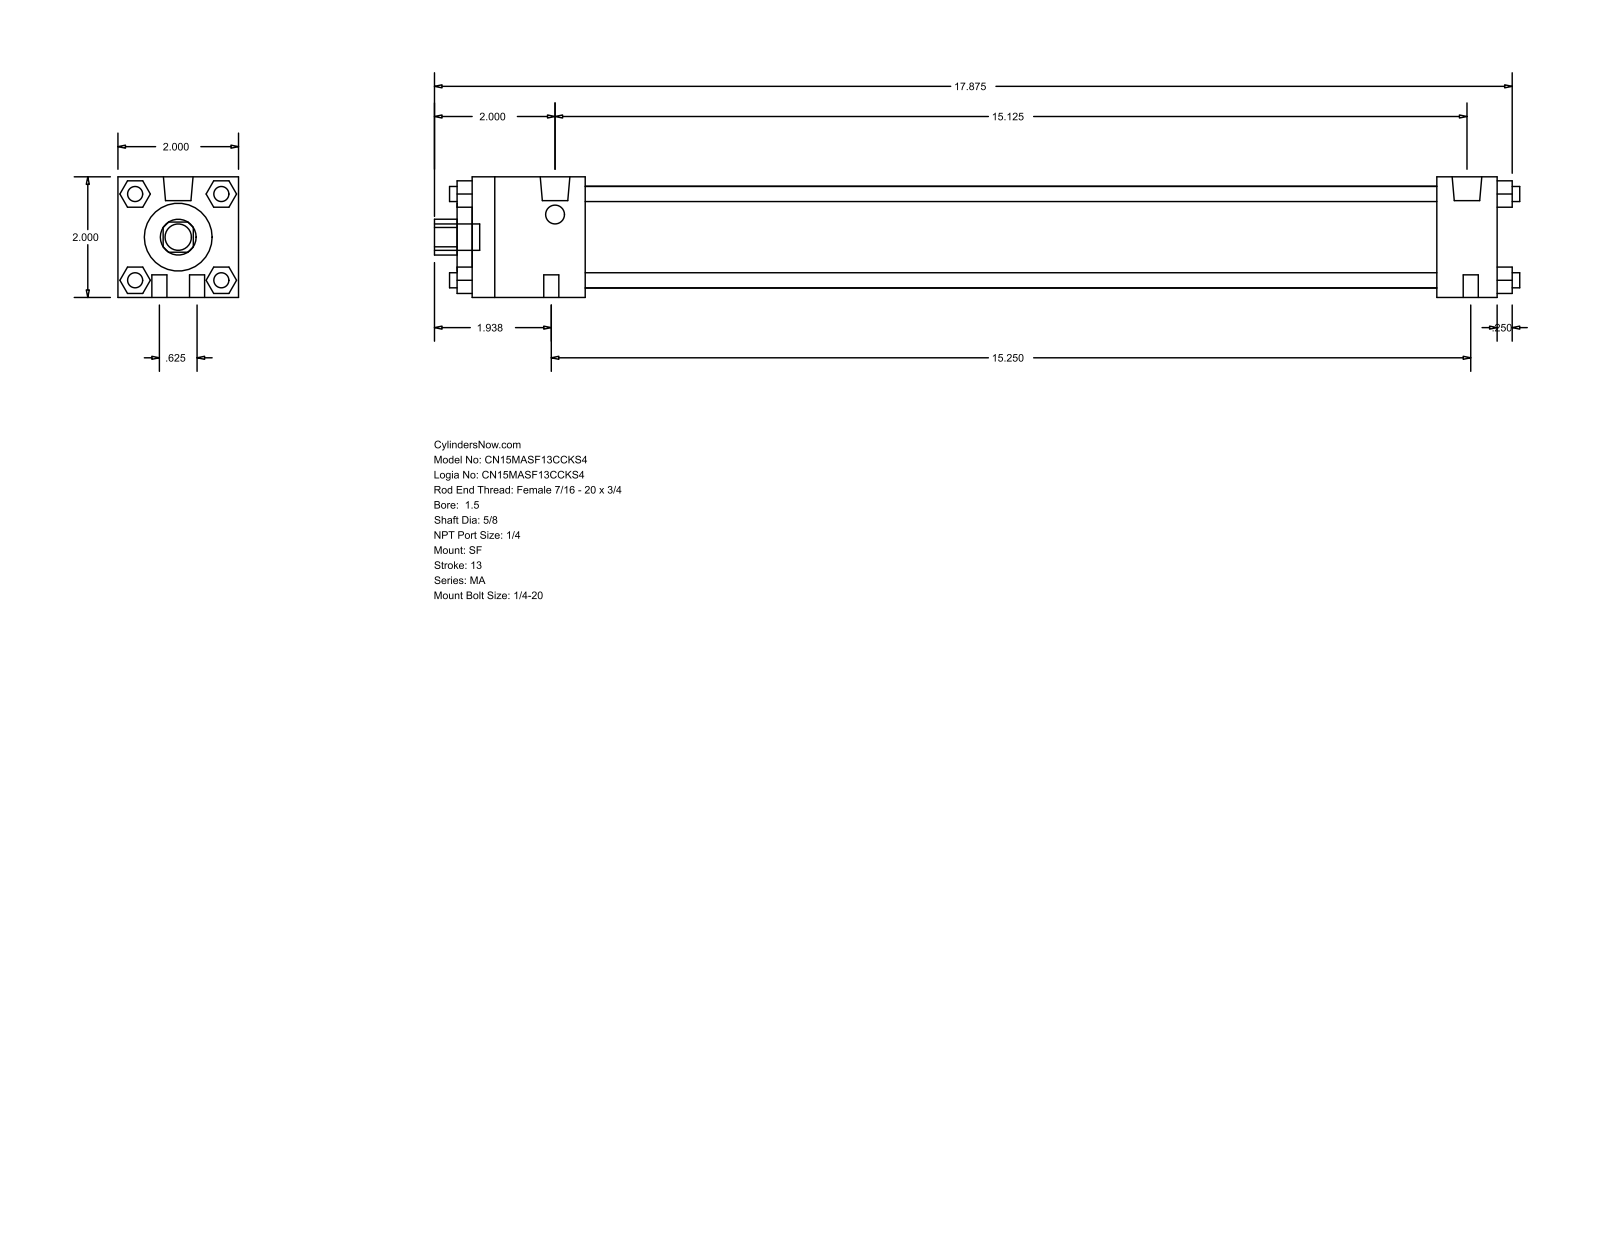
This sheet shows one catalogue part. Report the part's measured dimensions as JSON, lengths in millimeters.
{"part_name": "MA_SF__0150_0.625", "step_written_by": "GSSL Pune (CONFIG_CONTROL_DESIGN)", "units": "millimeters", "bodies": {"solids": 0, "faces": 124, "planar": 94, "cylindrical": 30, "other": 0}, "overall_size": [457.2, 50.8, 50.8], "round_holes": [[15.88, 1], [28.57, 1], [42.93, 1]], "round_bosses_or_shafts": [[6.35, 8], [12.49, 2], [7.94, 2], [11.11, 1]], "partial_cylinders_radius": [[7.54, 1]], "face_to_face_distances": [50.8, 431.8, 47.62, 406.39, 358.77, 384.18, 25.41, 6.35, 438.15, 53.97]}
